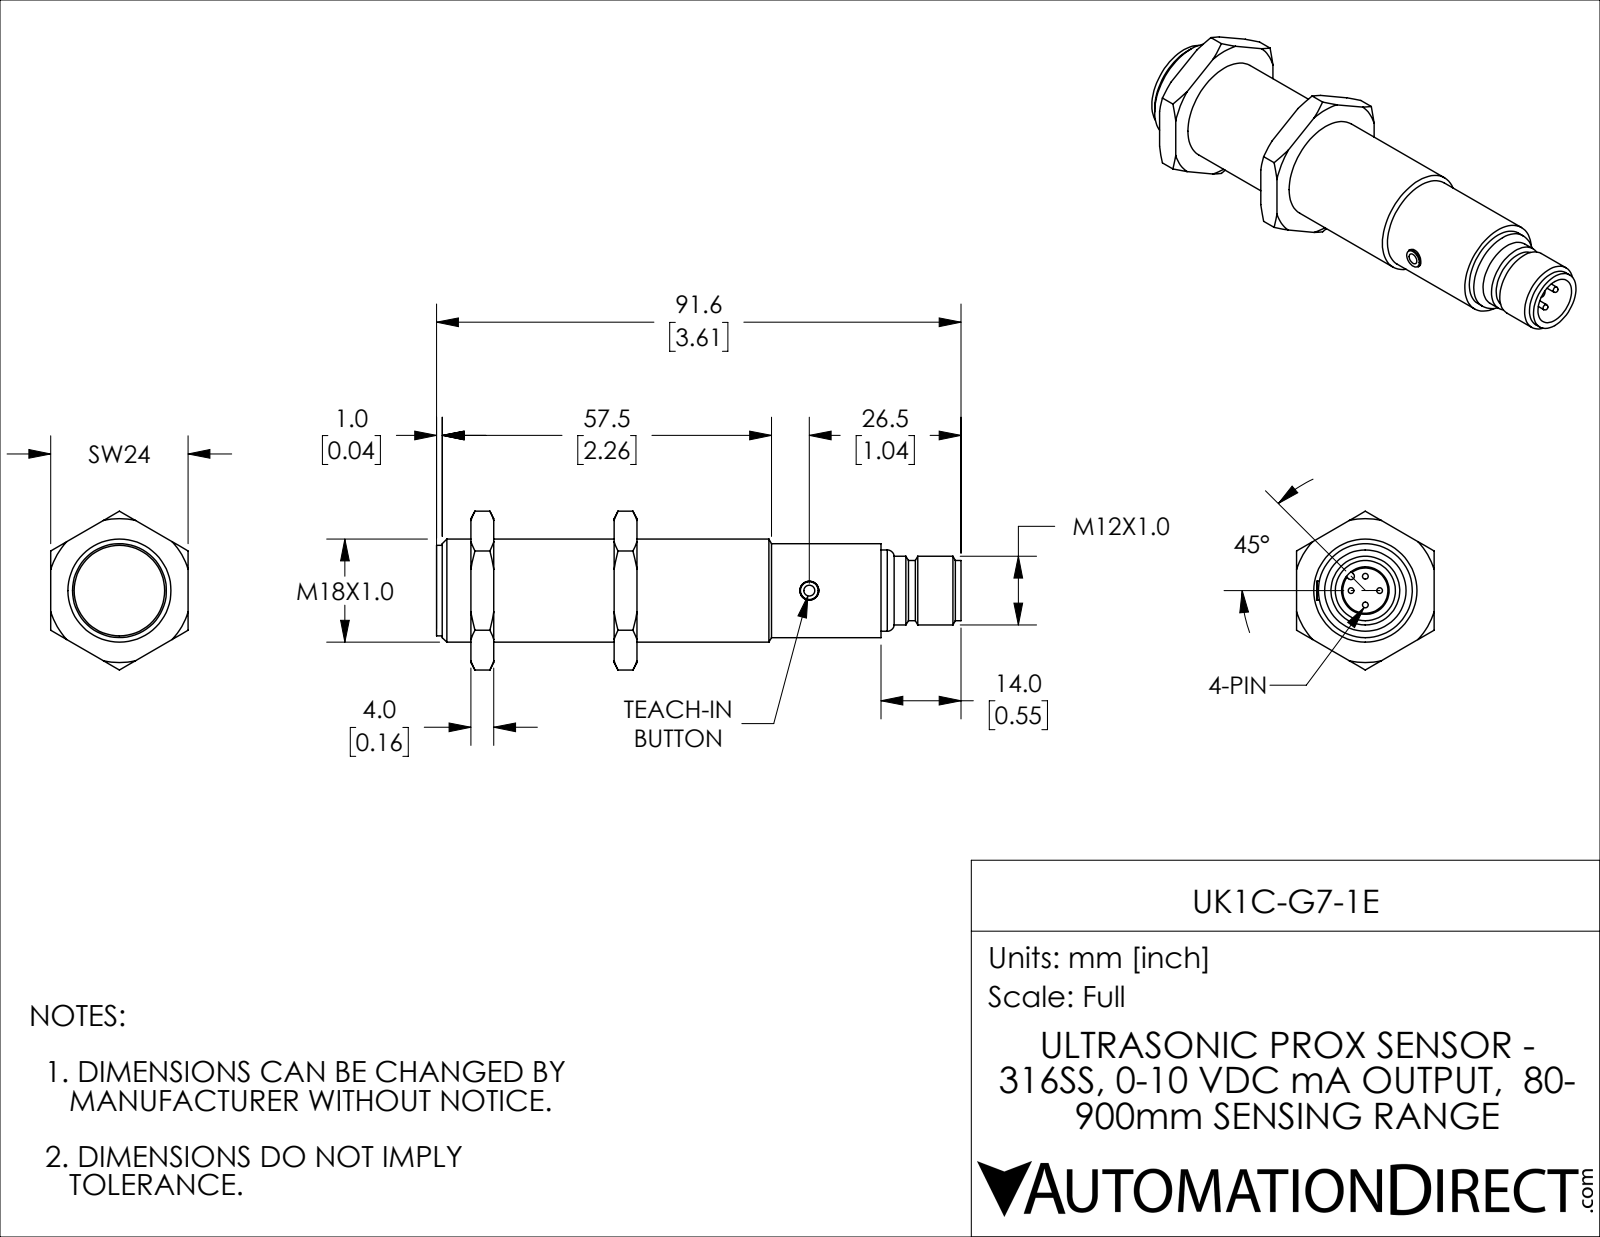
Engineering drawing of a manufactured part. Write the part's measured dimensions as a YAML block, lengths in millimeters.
part_name: "UK1C-G7-1E"
step_written_by: "SolidWorks 2018 (AUTOMOTIVE_DESIGN)"
units: millimeters
bodies: {solids: 4, faces: 113, planar: 27, cylindrical: 35, other: 51}
overall_size: [91.6, 27.7, 24]
volume: 21930
surface_area: 7723
round_holes:
  - {diameter: 3.3, count: 1}
  - {diameter: 8.3, count: 1}
  - {diameter: 18, count: 1}
round_bosses_or_shafts:
  - {diameter: 1, count: 4}
  - {diameter: 16.4, count: 1}
  - {diameter: 15.8, count: 1}
  - {diameter: 14.2, count: 1}
  - {diameter: 12, count: 1}
  - {diameter: 10.5, count: 1}
partial_cylinders:
  - {radius: 0.6, count: 1}
face_to_face_distances: [25, 4, 24, 29, 21, 6, 10, 31, 35, 77.6]
